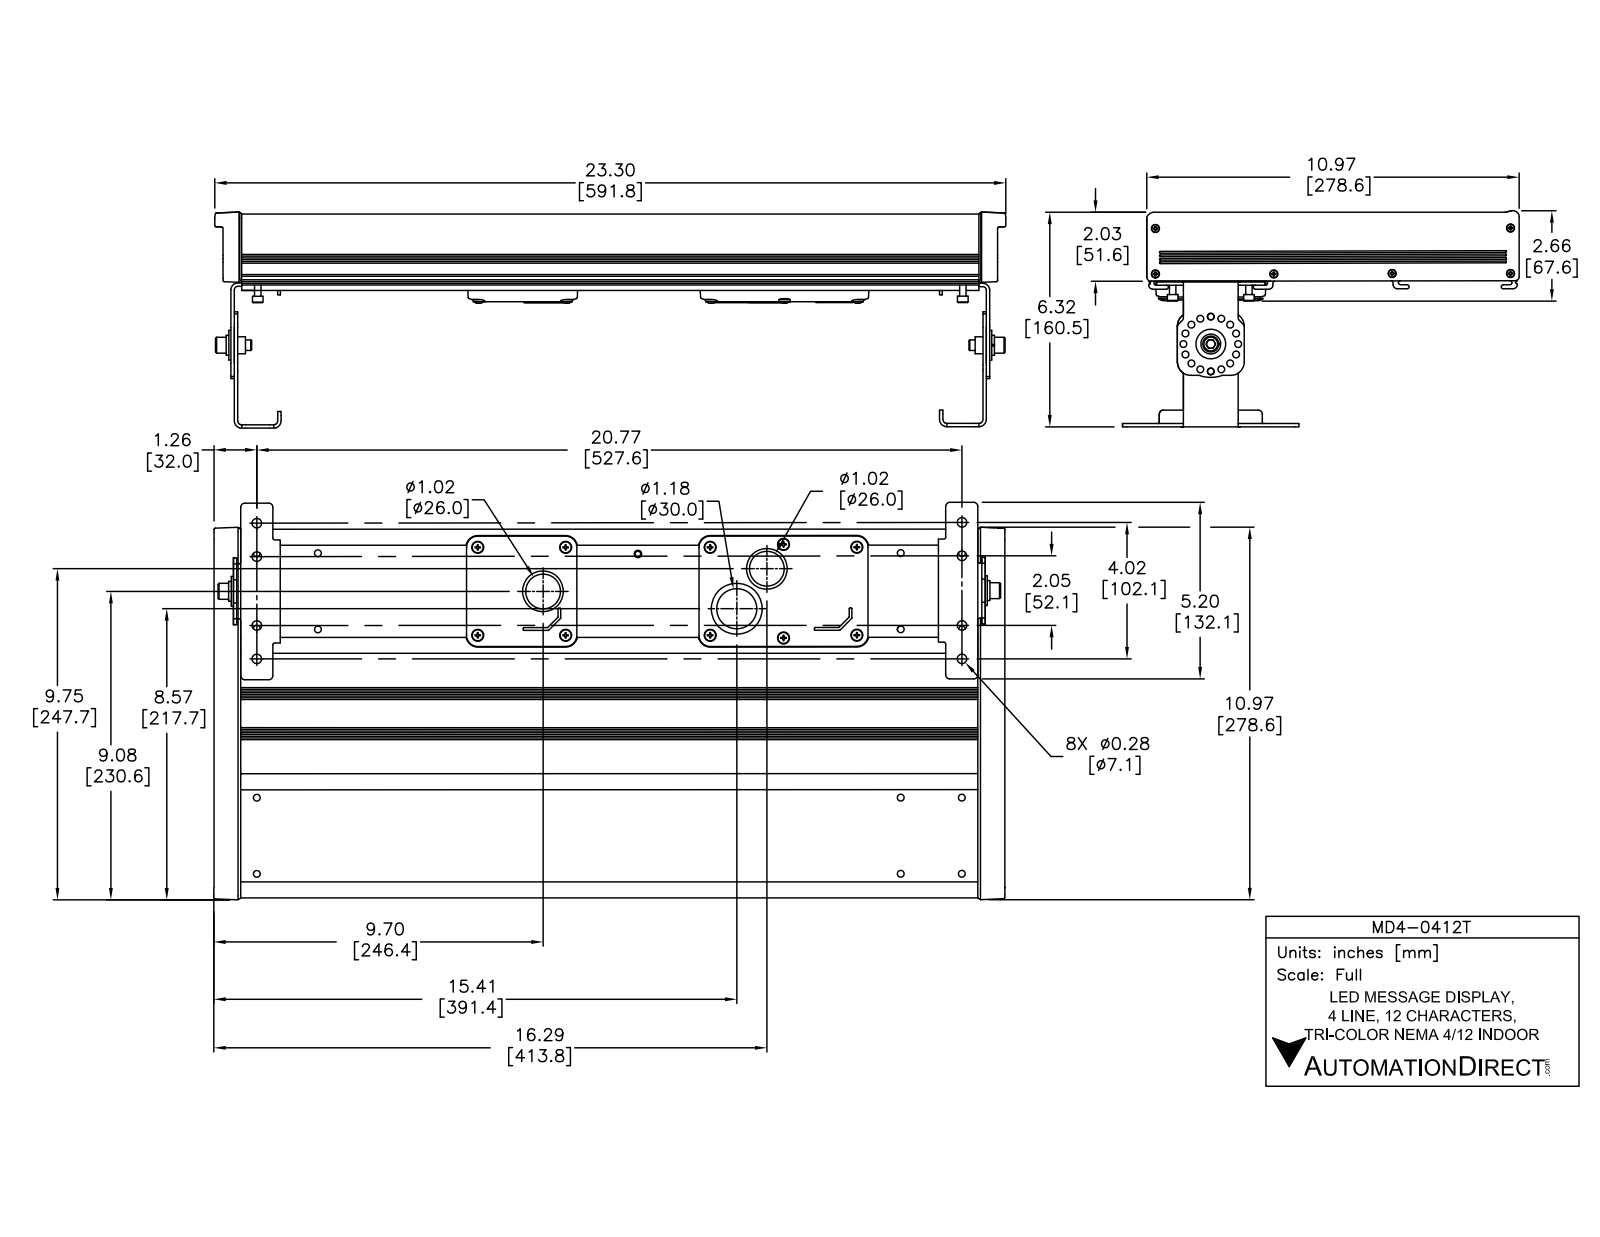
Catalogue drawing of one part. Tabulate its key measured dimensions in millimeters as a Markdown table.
| quantity | value |
| --- | --- |
| part name | MD4-0412T |
| STEP written by | SolidWorks 2017 (AUTOMOTIVE_DESIGN) |
| units | millimeters |
| bodies | 39 solids, 5737 faces (1603 planar, 1952 cylindrical, 2182 other) |
| overall size | 599.5 × 296.8 × 161.6 |
| volume | 2 224 000 mm³ |
| surface area | 1 618 000 mm² |
| round holes (diameter × count) | 5.1 × 22, 7.1 × 12, 3.5 × 10, 3 × 6, 3.7 × 6, 4.8 × 6, 6.8 × 6, 4 × 4, 13.5 × 3, 15.3 × 3, 20 × 3, 20.4 × 3 |
| round bosses / shafts (diameter × count) | 30 × 3, 28 × 3, 25 × 3, 24.2 × 3, 21.3 × 3, 20.5 × 3, 19.9 × 3, 17.2 × 2 |
| partial cylindrical surfaces (radius × count) | 0.5 × 388, 0.5 × 212, 0.3 × 142, 0.3 × 66, 1 × 66, 3 × 64, 0.7 × 36, 1.1 × 30 |
| main face-to-face distances | 3, 44.1, 2.7, 0.4, 3.1, 2.6, 47.1, 44.5, 47.2, 41.1 |
| hole center spacings | 34.1, 29, 8, 20.5, 22.8, 37.9, 15.7, 40.2 |
